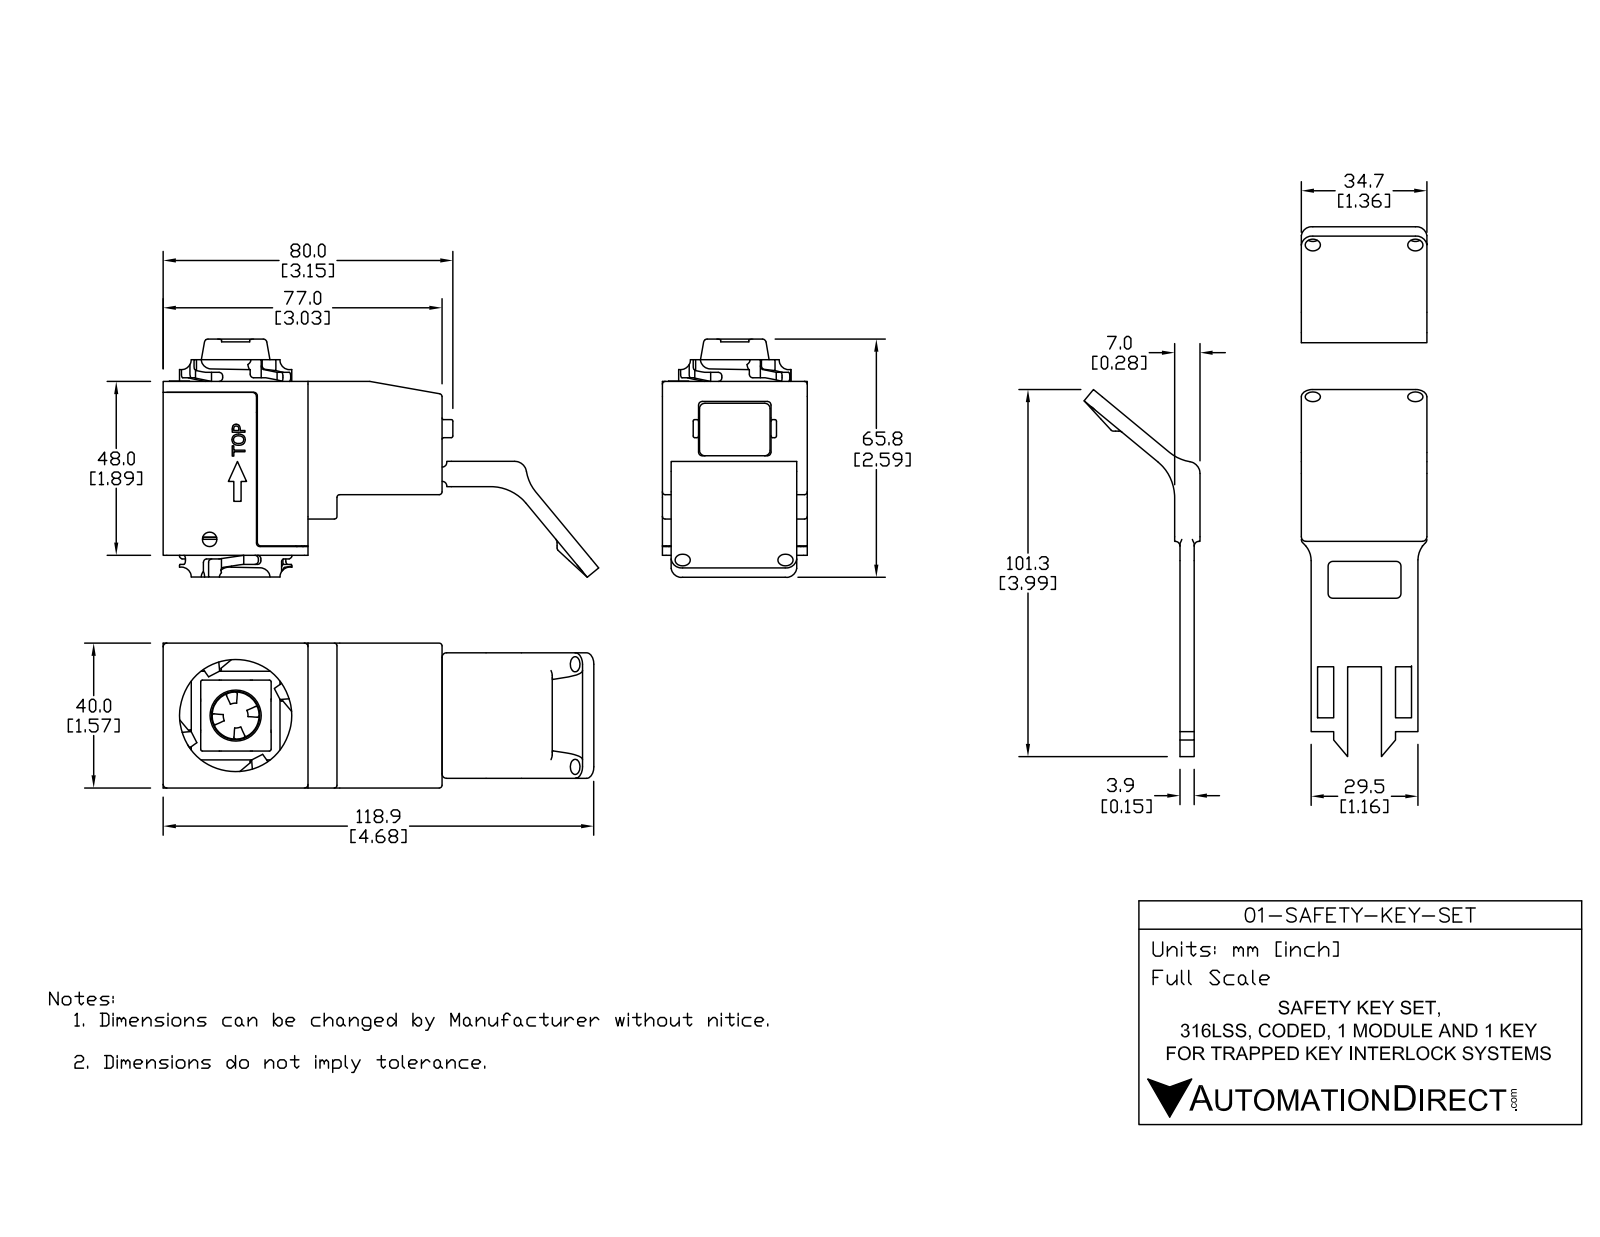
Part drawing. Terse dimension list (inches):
name: 01-SAFETY-KEY-SET
written by: SolidWorks 2017 (AUTOMOTIVE_DESIGN)
unit: in
bodies: 8 solids, 1965 faces (814 planar, 389 cylindrical, 762 other)
size: 4.61 × 2.686 × 1.585
volume: 9.339 in³; area: 51.04 in²
holes: 3× ⌀0.157, 2× ⌀0.217, 1× ⌀0.079, 1× ⌀0.097, 1× ⌀0.134
bosses: 1× ⌀0.394, 1× ⌀0.161
rounds: 183× R0.02, 45× R0.006, 27× R0.039, 18× R0.018, 17× R0.03, 13× R0.079, 4× R0.059, 4× R0.098
face distances: 1.575, 1.89, 2.362, 0.472, 0.659, 1.23, 1.703, 1.1, 1.573, 0.059
hole spacings: 0.571, 0.772, 0.965, 1.054, 1.181
